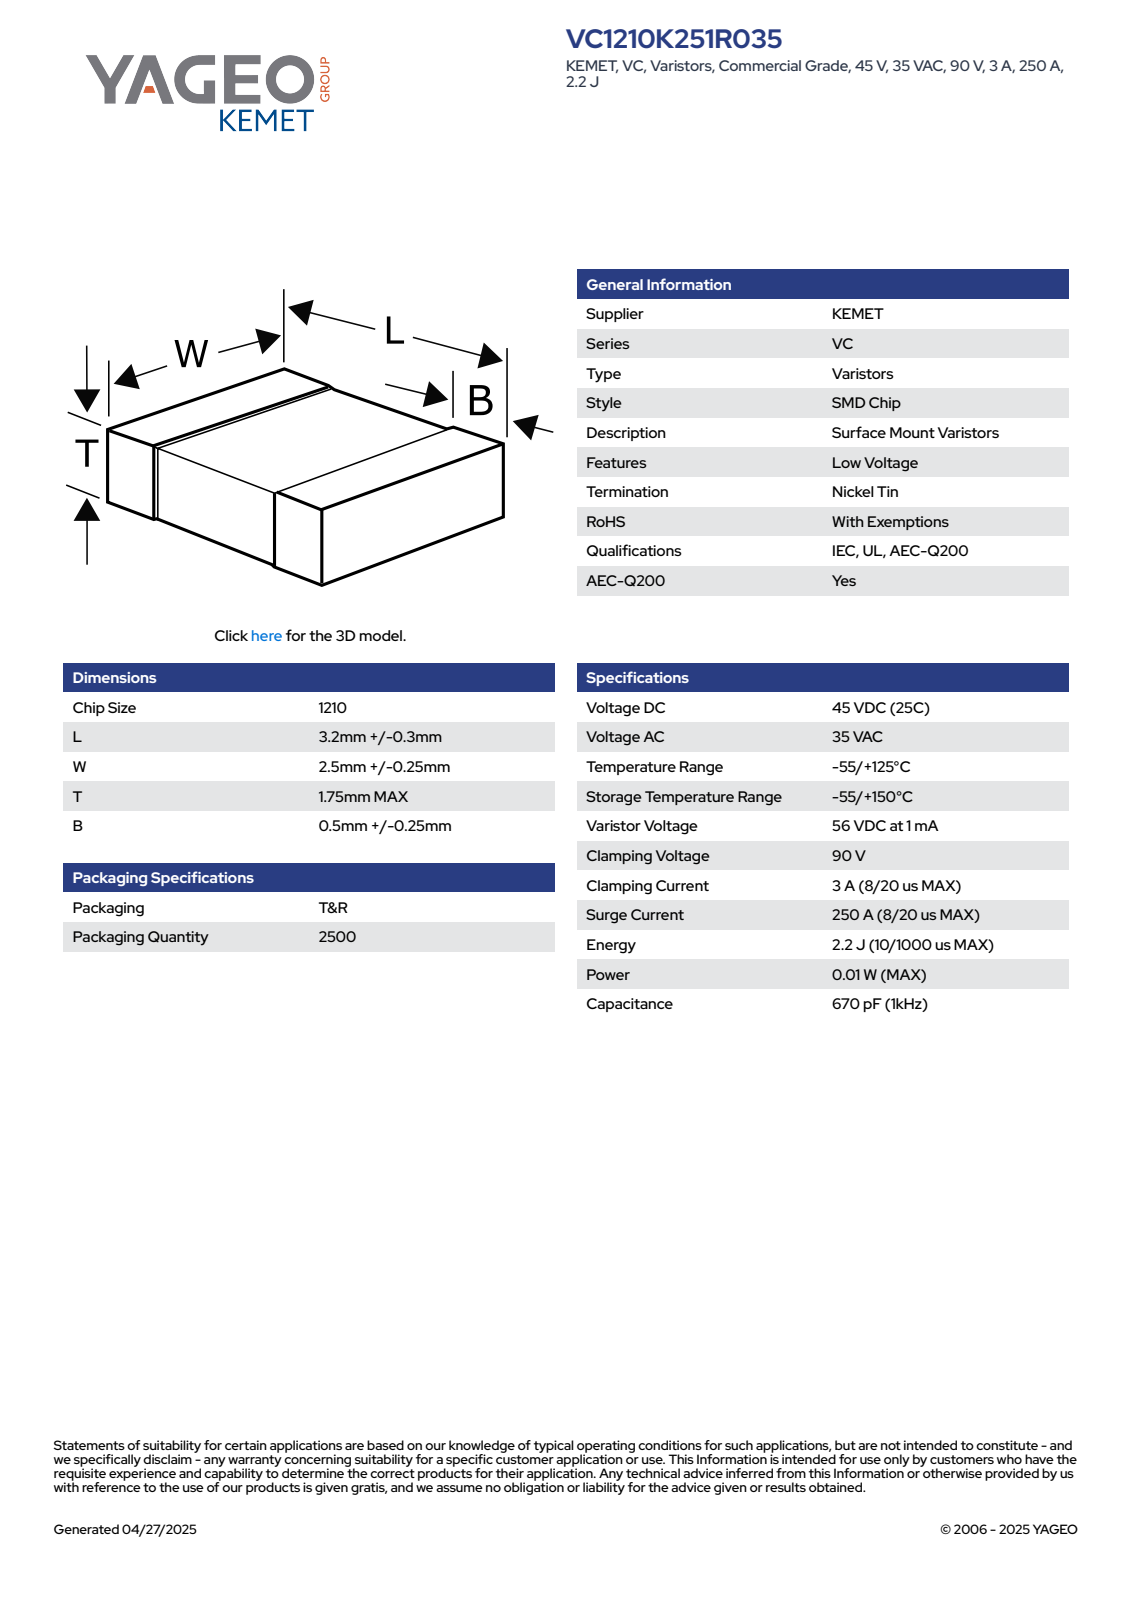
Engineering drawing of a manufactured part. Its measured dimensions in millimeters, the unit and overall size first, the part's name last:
Units: millimetres
Overall size (bounding box): 3.5 × 2.75 × 1.45
Main face-to-face distances: 1.39, 1.33, 3.5, 2.69, 1.45, 2.63, 2.75, 1.4, 1.34, 1.49
Volume: 13 mm³ · Surface area: 37 mm²
Bodies: 4 solids, 125 faces (71 planar, 38 cylindrical, 16 other)
Part name (STEP PRODUCT): VS_SMD_1210_L3.50W2.75T1.45B0.75
STEP written by: SolidWorks 2014 (AUTOMOTIVE_DESIGN)
